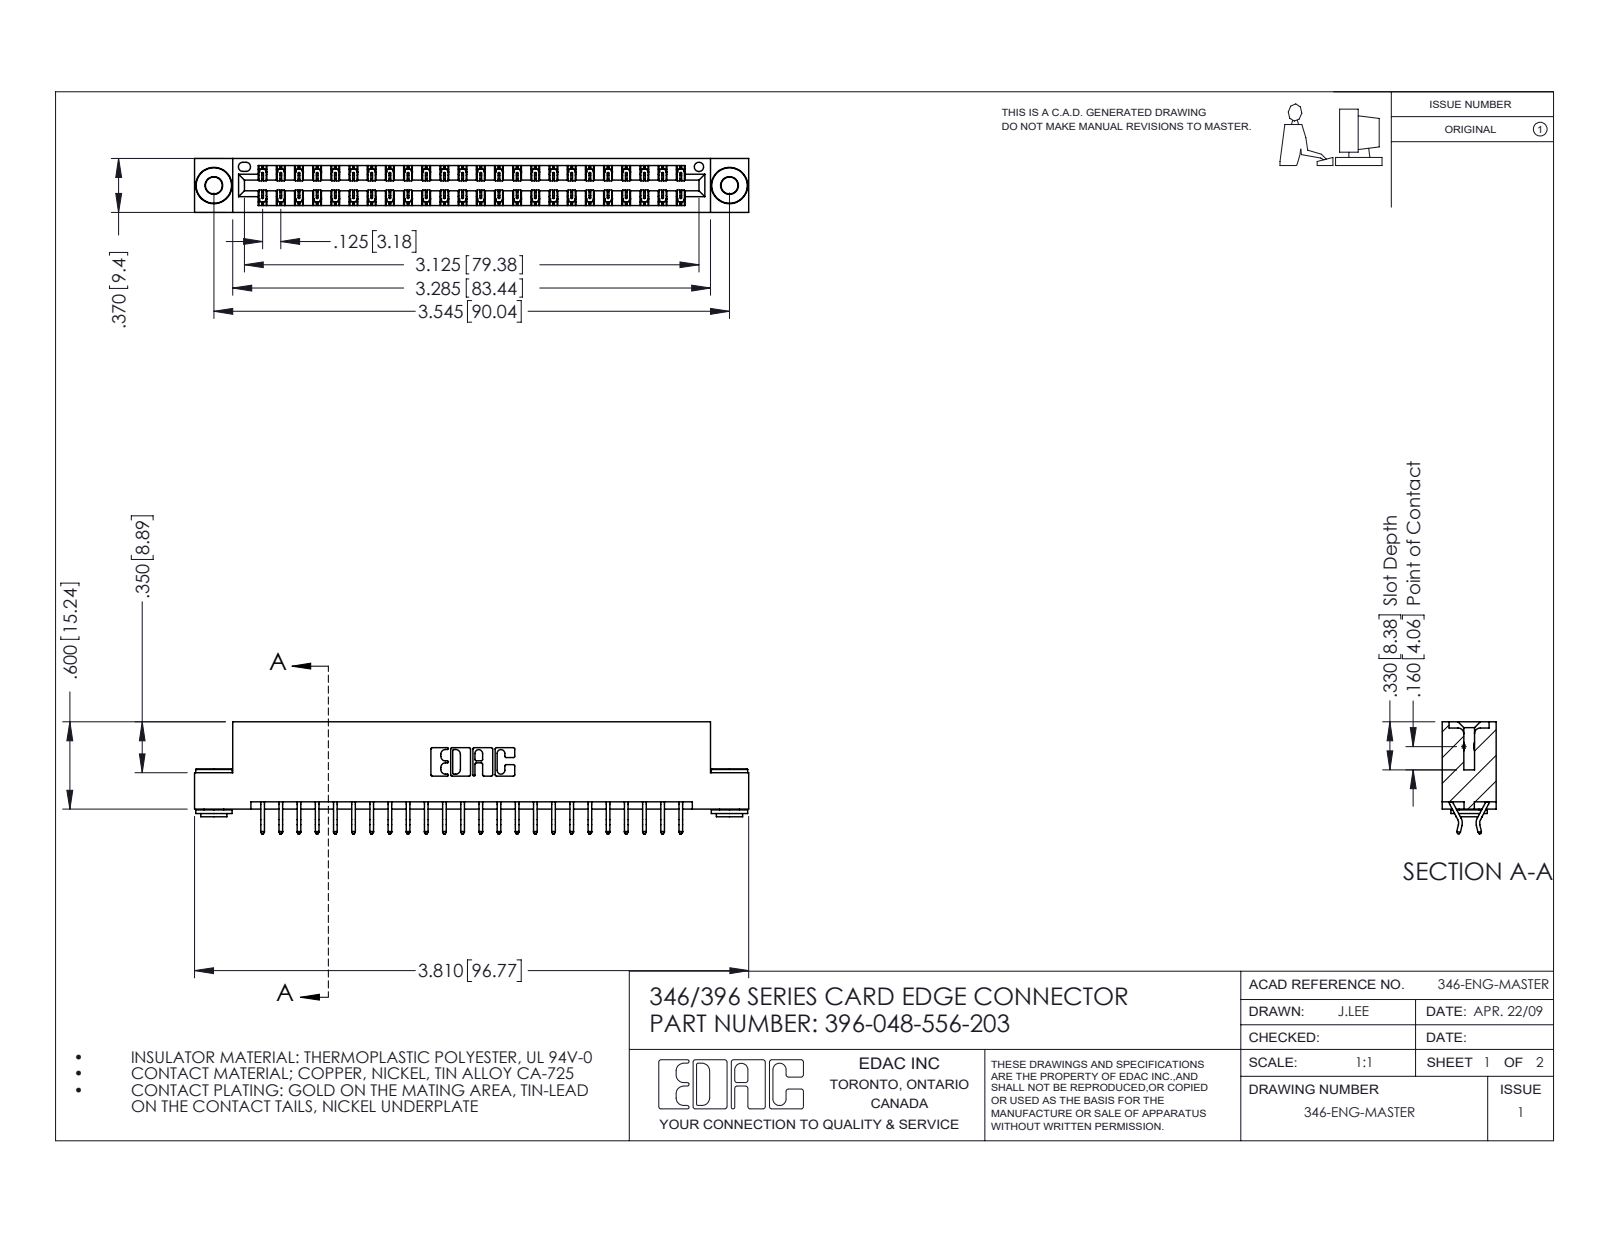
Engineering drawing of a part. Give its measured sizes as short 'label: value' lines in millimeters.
name: 345-250-002_345-250-002-102; 345-292-001_556 Tail; 396-048-556-203; 346 Part_Flush Mounting Lugs - 0.156 Dia-TH
written by: SolidWorks 2016 (CONFIG_CONTROL_DESIGN)
unit: mm
bodies: 51 solids, 2944 faces (1958 planar, 978 cylindrical, 8 other)
size: 96.8 × 19.6 × 9.4
volume: 9 310 mm³; area: 12 690 mm²
holes: 2× ⌀2.9, 2× ⌀4, 1× ⌀1.6
bosses: 2× ⌀6.4, 2× ⌀4.6, 2× ⌀3.5
rounds: 72× R0.2, 22× R0.3, 6× R0.2, 6× R0.8, 3× R0.7, 2× R0.3, 2× R0.4, 2× R0.6
face distances: 1.2, 8.2, 6.4, 9.4, 0.6, 1.8, 7.6, 7, 3.8, 5.6
hole spacings: 6.2, 84.8, 90
